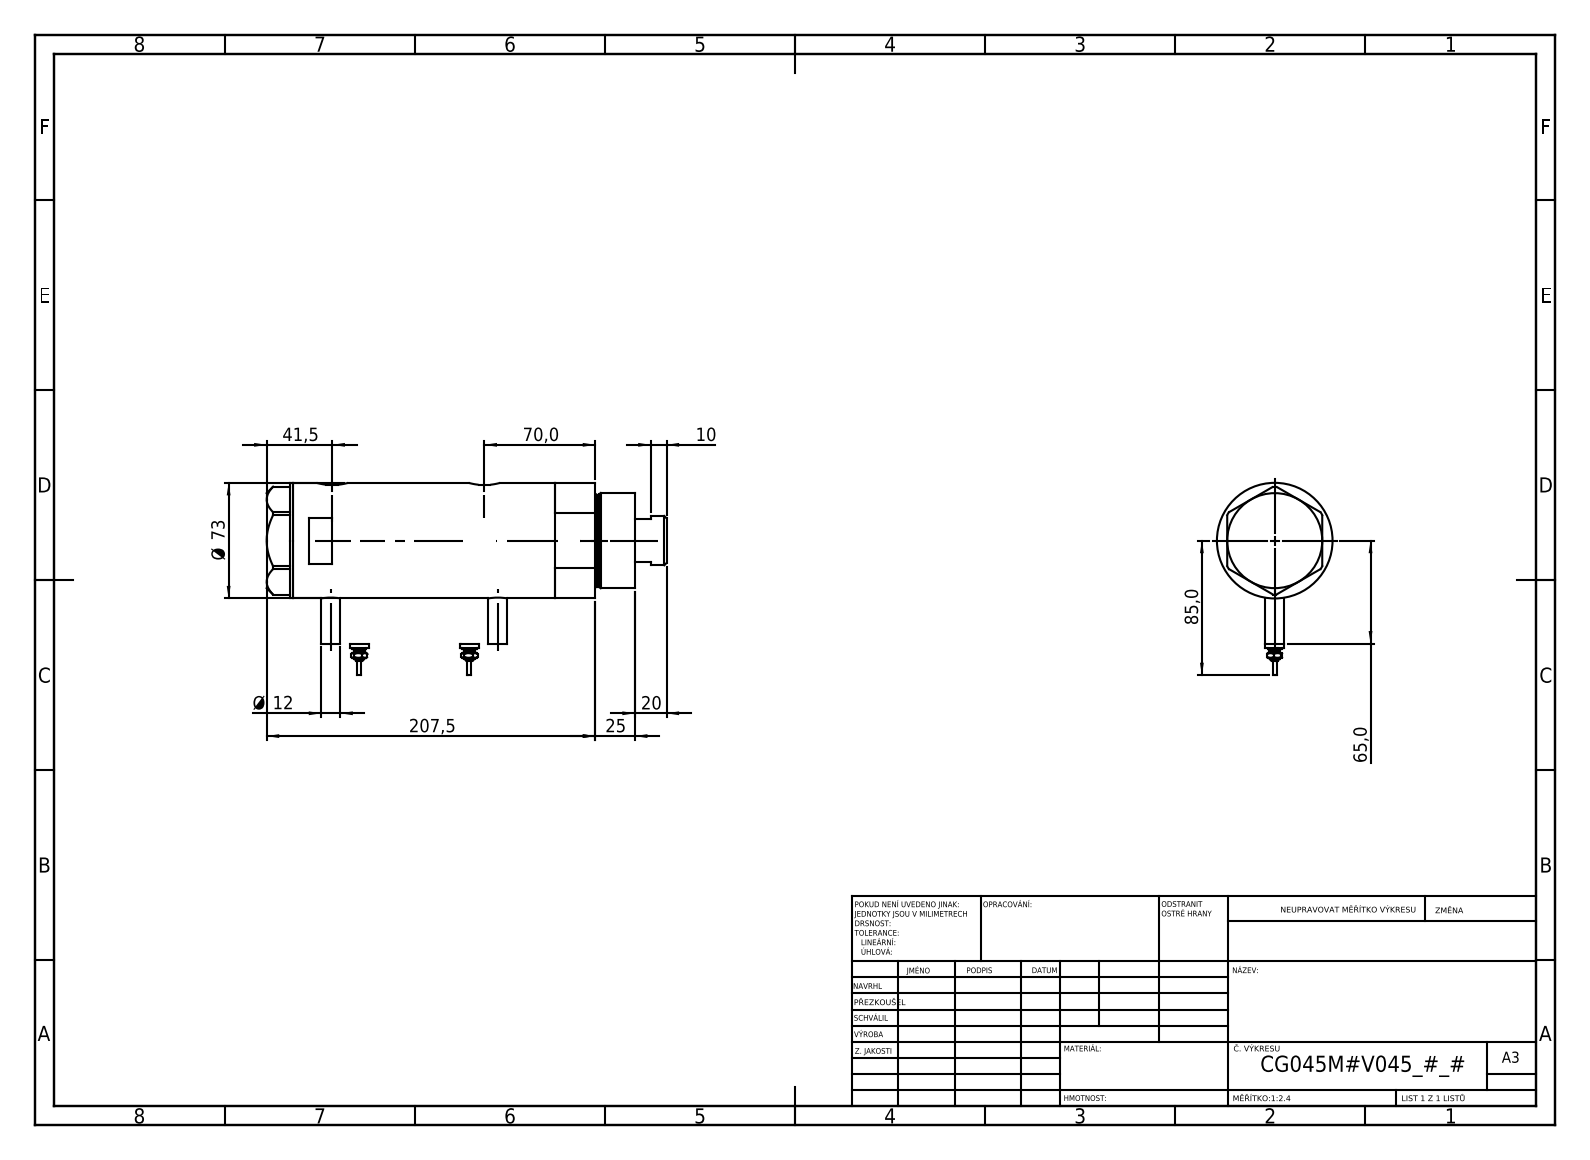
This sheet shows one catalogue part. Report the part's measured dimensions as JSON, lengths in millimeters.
{"part_name": "V270CG_MIDDLE; Switch; V270CG_BACK; V270CG_VC (+1 more)", "step_written_by": "SolidWorks 2019 (CONFIG_CONTROL_DESIGN)", "units": "millimeters", "bodies": {"solids": 6, "faces": 212, "planar": 77, "cylindrical": 71, "other": 64}, "overall_size": [252.5, 121.5, 73], "volume_mm3": 896090, "surface_area_mm2": 151933, "round_holes": [[12.5, 2], [13.16, 2], [10.5, 1], [32, 1], [33.5, 1], [45, 1], [48, 1], [64, 1]], "round_bosses_or_shafts": [[12, 4], [9, 2], [7, 2], [4.5, 2], [2.5, 2], [73, 1], [60, 1], [58, 1]], "partial_cylinders_radius": [[10, 2]], "face_to_face_distances": [95, 121, 26, 16.5, 42.5, 137.5, 2, 216, 232.5, 190], "hole_center_spacings": [1, 8.5, 96, 97, 104.5, 105.5]}
